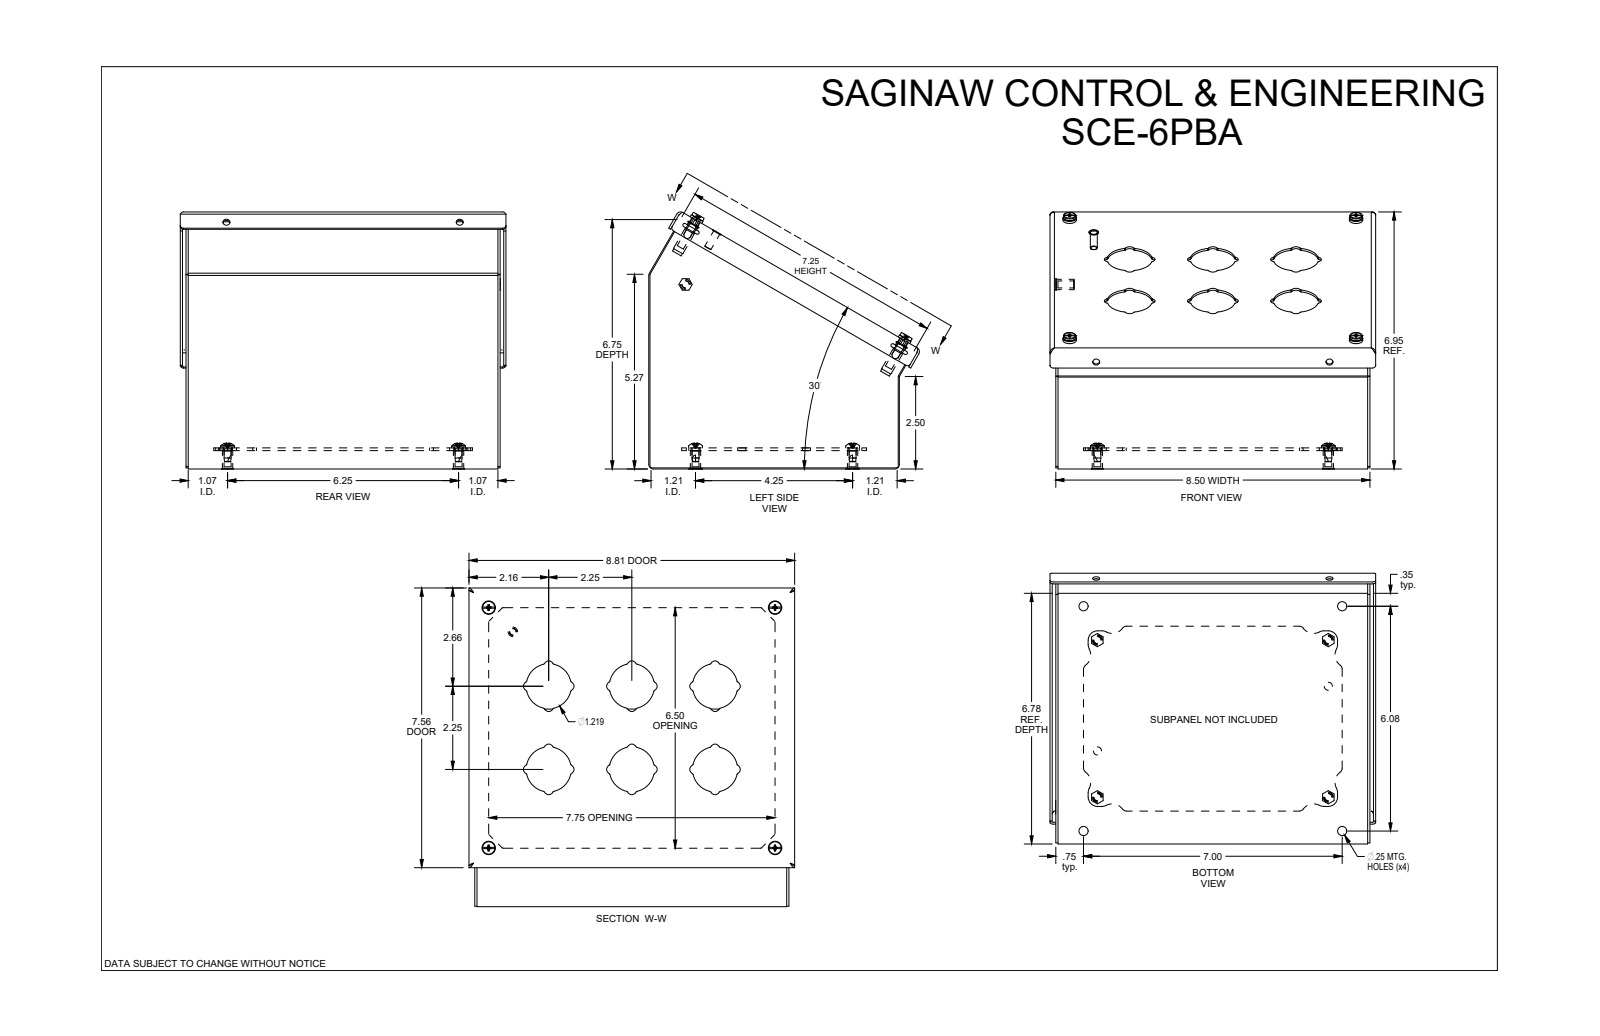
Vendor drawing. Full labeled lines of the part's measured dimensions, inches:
Part name (STEP PRODUCT): SCE-6PBA
STEP written by: SolidWorks 2021 (AUTOMOTIVE_DESIGN)
Units: inches
Bodies: 3 solids, 598 faces (203 planar, 317 cylindrical, 78 other)
Overall size (bounding box): 8.813 × 7.345 × 6.978
Volume: 21.2 in³ · Surface area: 696.1 in²
Round holes (diameter × count): ⌀0.25 ×16, ⌀0.19 ×9, ⌀0.22 ×4, ⌀0.266 ×4, ⌀0.317 ×4, ⌀0.218 ×2
Round bosses / shafts (diameter × count): ⌀0.28 ×5, ⌀0.362 ×4, ⌀0.34 ×4, ⌀0.292 ×4, ⌀0.27 ×4, ⌀0.26 ×4, ⌀0.256 ×1, ⌀0.188 ×1
Partial cylindrical surfaces — rounded edges, fillets, slot ends (radius × count): R0.04 ×48, R0.125 ×32, R0.25 ×12, R0.01 ×8, R0.03 ×8, R0.06 ×8, R0.115 ×8, R0.24 ×8
Main face-to-face distances: 0.06, 8.44, 6.72, 8.5, 8.38, 0.436, 0.496, 0.571, 0.511, 0.075
Hole centre spacings: 7.75, 6.5, 6.505, 10.115, 0.125, 0.949, 0.989, 4.25
